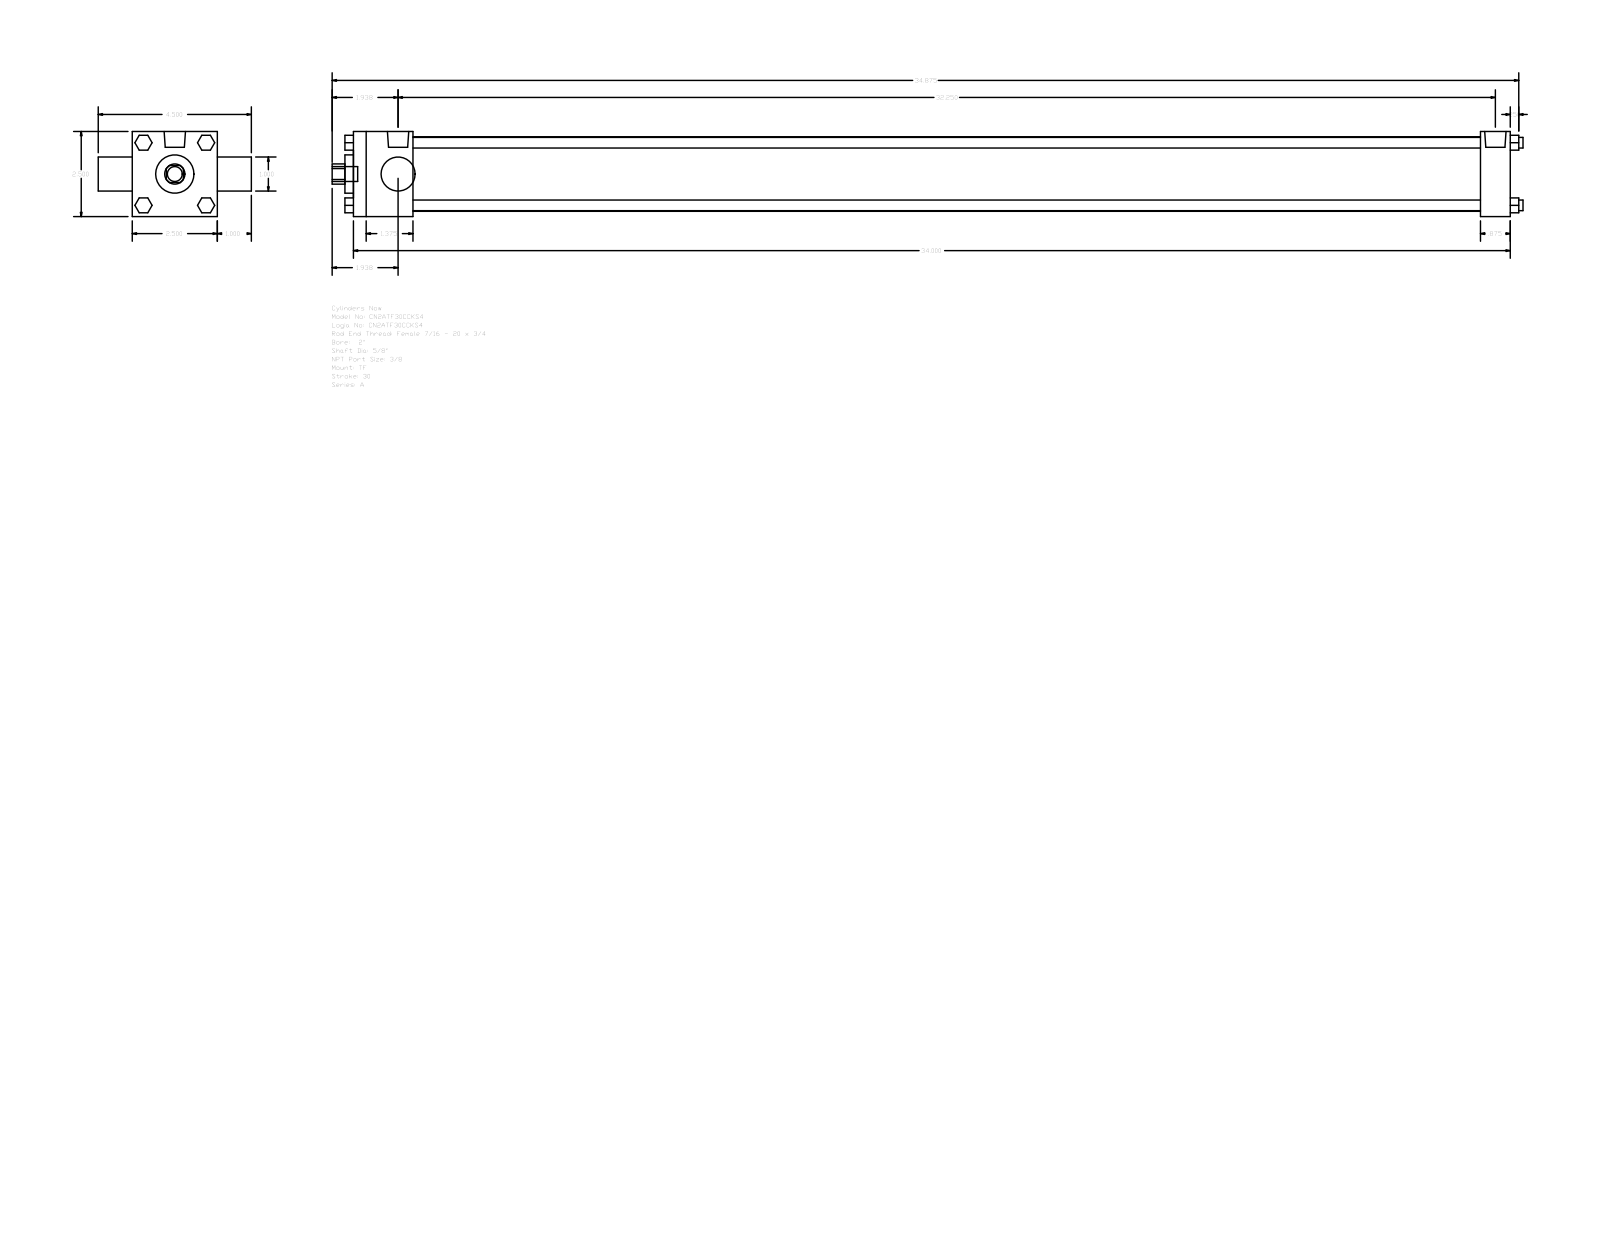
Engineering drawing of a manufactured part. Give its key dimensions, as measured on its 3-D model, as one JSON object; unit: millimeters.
{"part_name": "A_TF__0200_0.625", "step_written_by": "GSSL Pune (CONFIG_CONTROL_DESIGN)", "units": "millimeters", "bodies": {"solids": 0, "faces": 120, "planar": 92, "cylindrical": 28, "other": 0}, "overall_size": [889, 114.3, 63.5], "round_holes": [[15.88, 1], [25.4, 1], [28.57, 1], [55.63, 1]], "round_bosses_or_shafts": [[7.94, 4], [5.56, 3], [15.93, 2], [11.11, 1]], "partial_cylinders_radius": [[7.54, 1]], "face_to_face_distances": [63.5, 863.6, 44.45, 841.37, 796.92, 819.15, 22.23, 25.4, 88.9, 869.95]}
